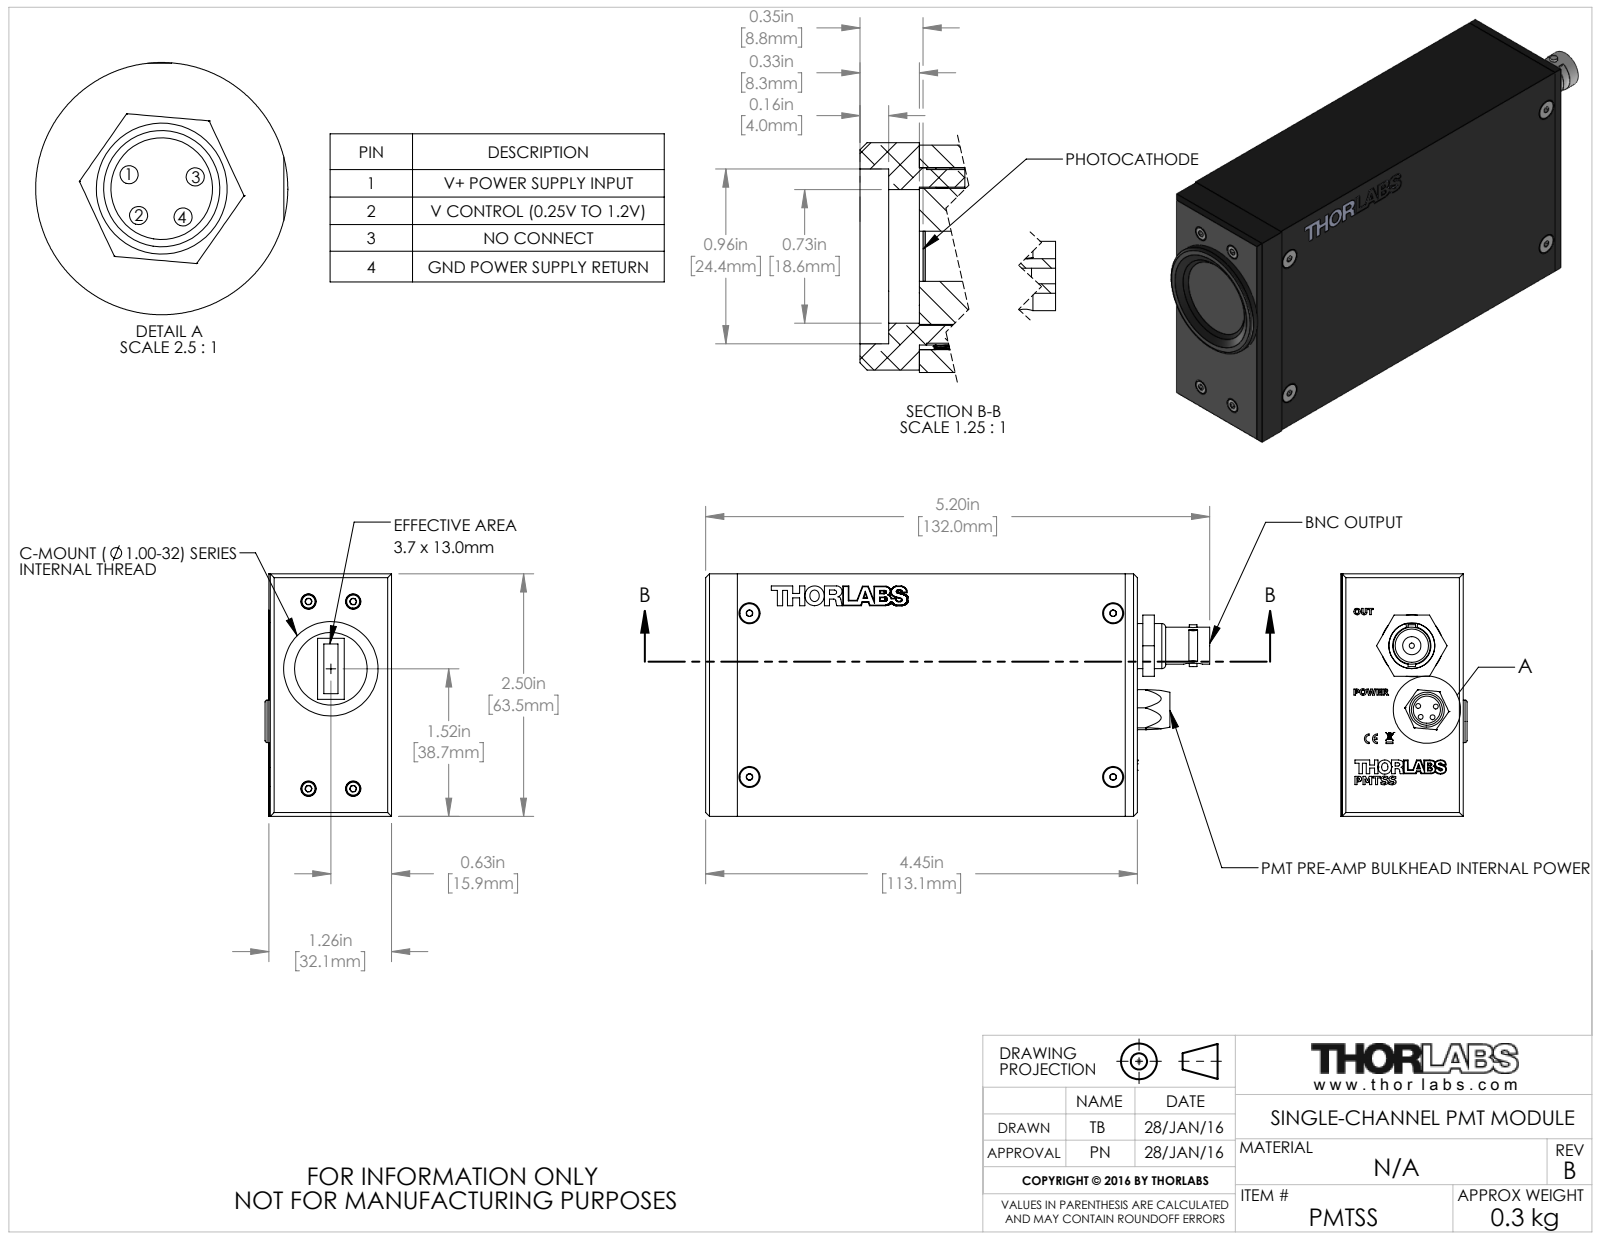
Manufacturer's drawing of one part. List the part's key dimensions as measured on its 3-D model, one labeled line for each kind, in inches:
Part name (STEP PRODUCT): TTN043089-E0W
STEP written by: SolidWorks 2014 (AUTOMOTIVE_DESIGN)
Units: inches
Bodies: 0 solids, 429 faces (237 planar, 57 cylindrical, 135 other)
Overall size (bounding box): 5.282 × 2.5 × 1.303
Round holes (diameter × count): ⌀0.05 ×4, ⌀0.157 ×4, ⌀0.054 ×1, ⌀0.32 ×1, ⌀0.343 ×1, ⌀0.64 ×1
Round bosses / shafts (diameter × count): ⌀0.197 ×4, ⌀1.195 ×1, ⌀0.472 ×1, ⌀0.437 ×1, ⌀0.382 ×1, ⌀0.28 ×1, ⌀0.079 ×1
Partial cylindrical surfaces — rounded edges, fillets, slot ends (radius × count): R0.059 ×2, R0.039 ×1
Main face-to-face distances: 1.25, 2.5, 4.452, 0.327, 4.125, 0.013, 4.327, 4, 0.125, 1.263
Hole centre spacings: 0.098, 0.461, 1.929, 1.983, 0.097, 0.115, 0.115, 0.122
